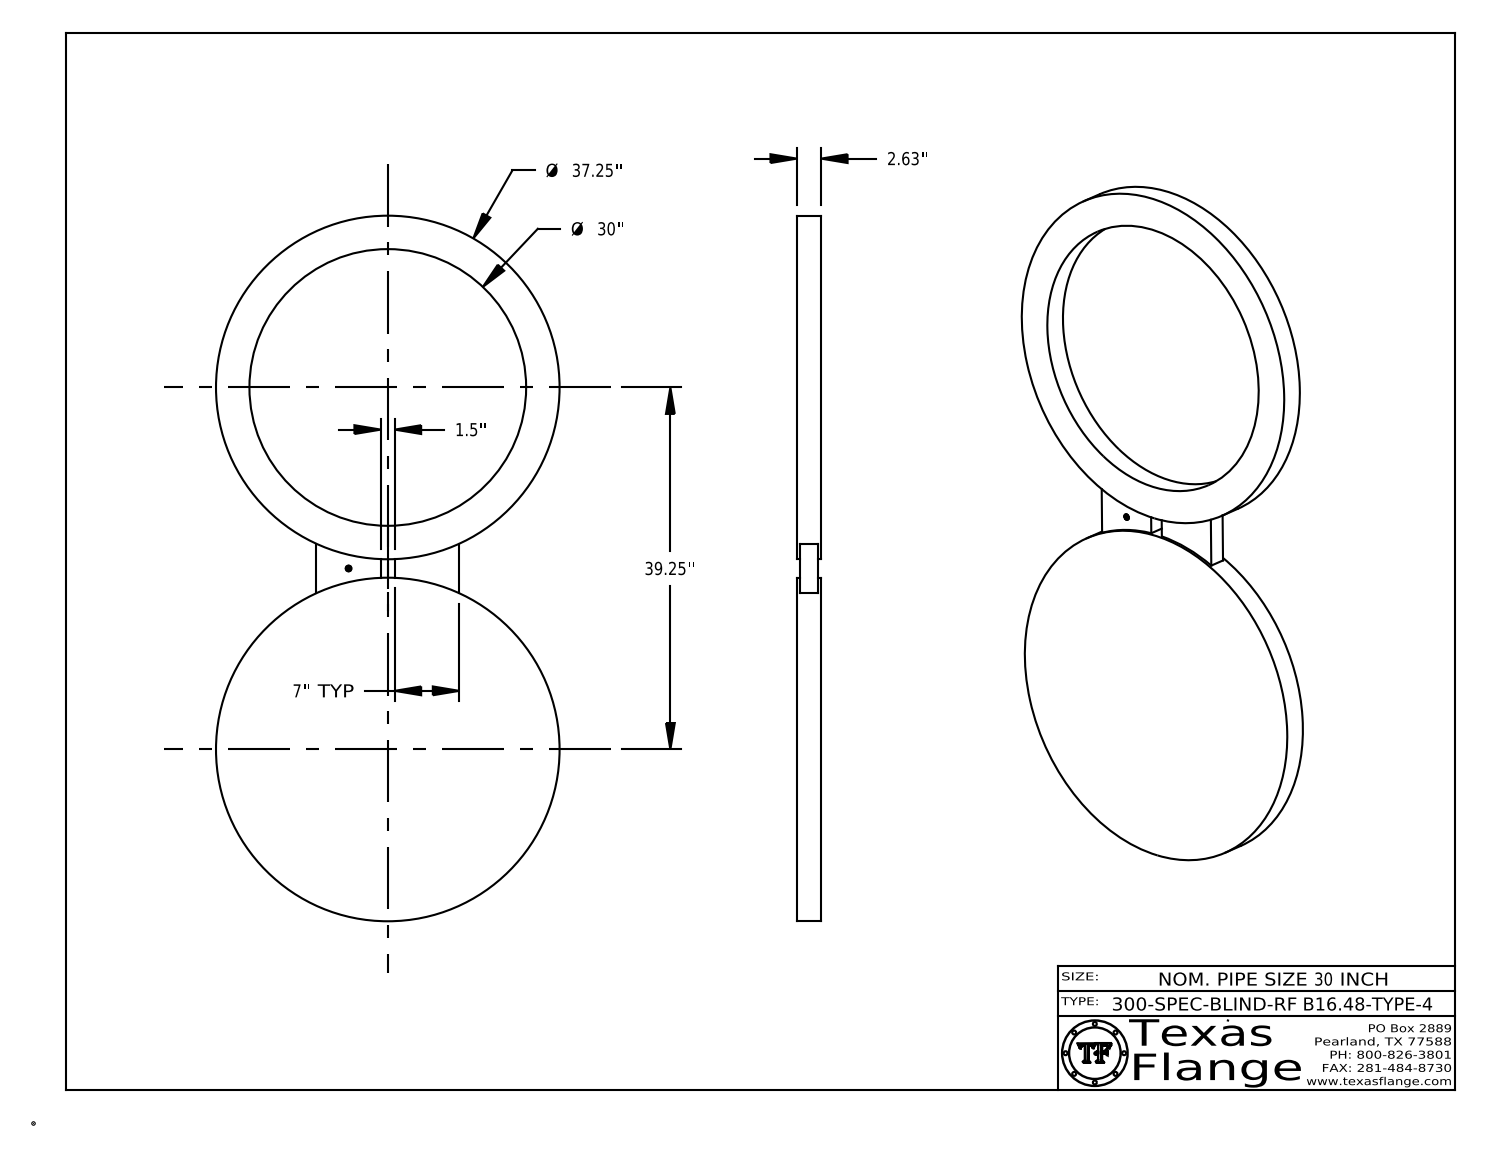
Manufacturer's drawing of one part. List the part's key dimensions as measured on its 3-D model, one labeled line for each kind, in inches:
Part name (STEP PRODUCT): 30-300-SPEC-BLIND-RF-B16.48-TYPE-4
STEP written by: CATIA V5 STEP AP214 (AUTOMOTIVE_DESIGN)
Units: inches
Bodies: 1 solid, 403 faces (377 planar, 26 cylindrical, 0 other)
Overall size (bounding box): 76.5 × 37.25 × 2.625
Volume: 3 955 in³ · Surface area: 3 870 in²
Round holes (diameter × count): ⌀0.625 ×1, ⌀30 ×1
Round bosses / shafts (diameter × count): ⌀0.038 ×8, ⌀37.25 ×2, ⌀0.492 ×1
Main face-to-face distances: 2.625, 0.328, 2.297, 1.969, 15.5, 7, 8.5, 1.5, 2.282, 1.954
Hole centre spacings: 20.08
